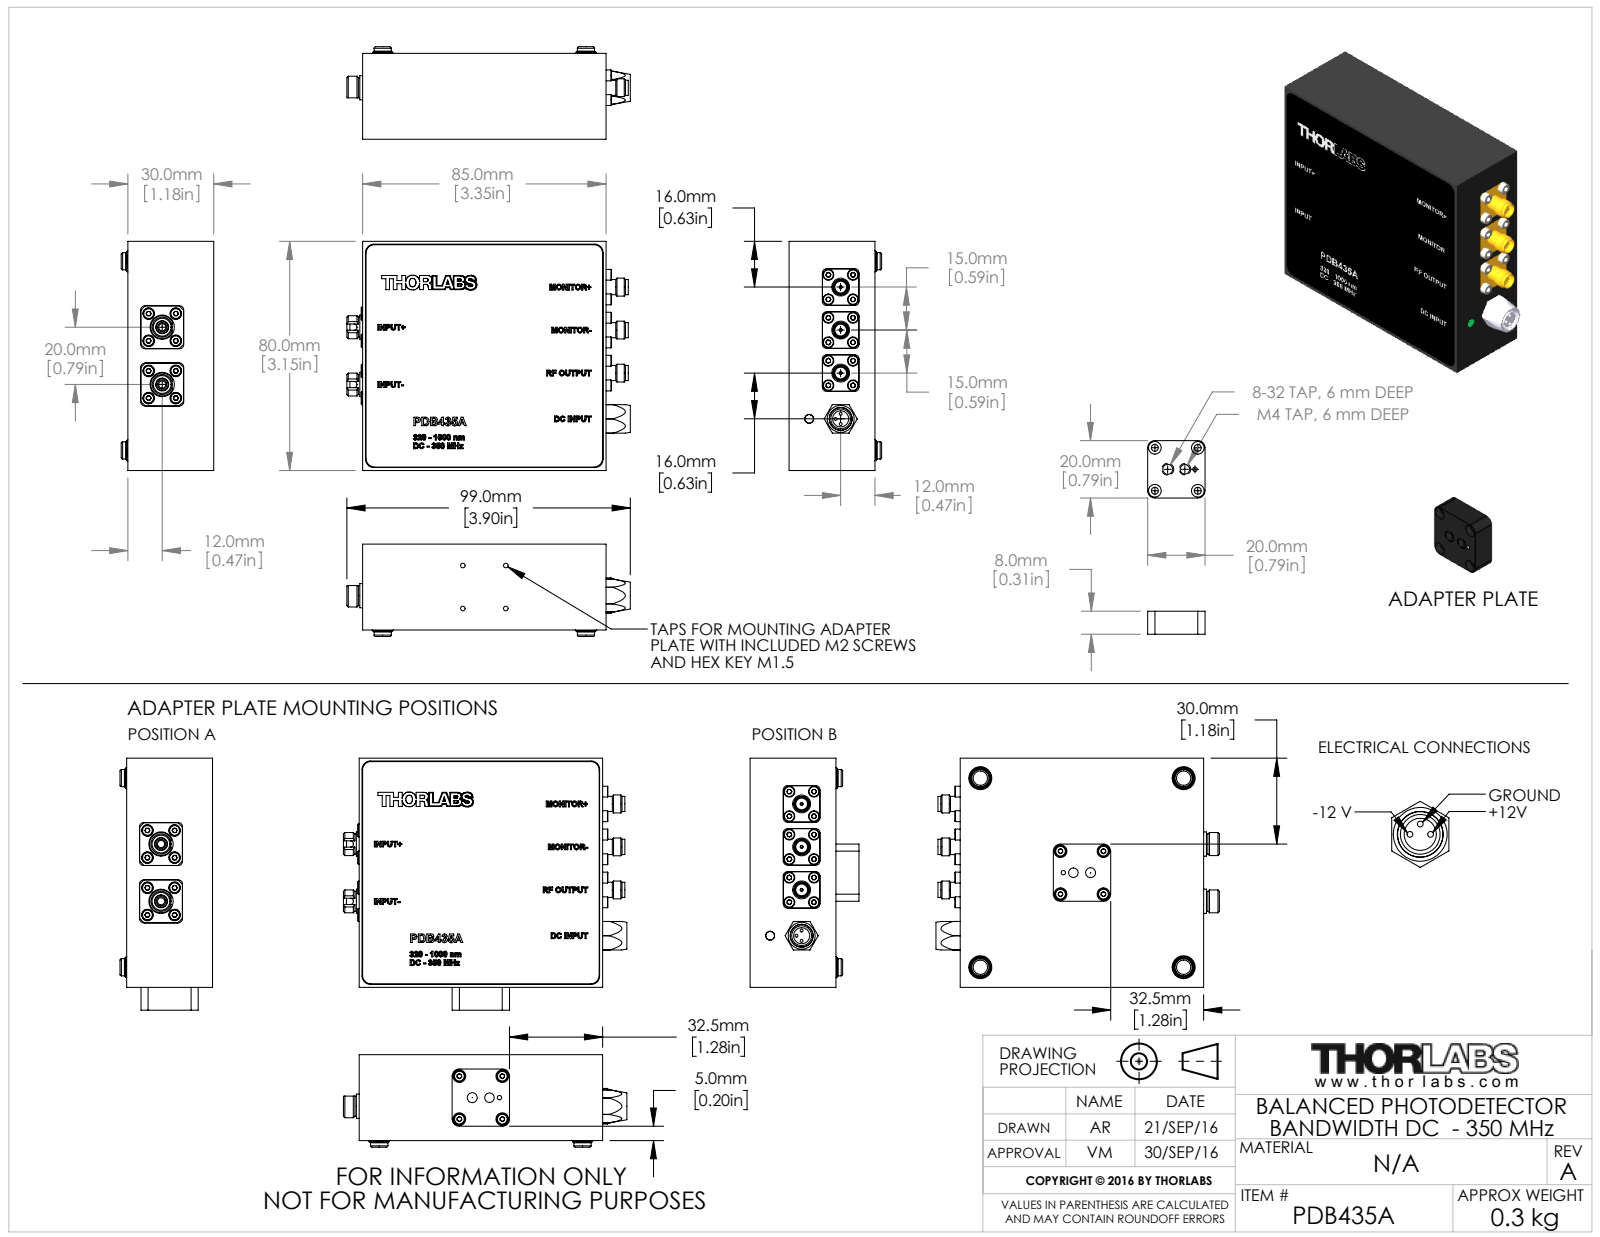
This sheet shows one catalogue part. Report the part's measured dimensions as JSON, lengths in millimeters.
{"part_name": "MTN005463-E0W", "step_written_by": "SolidWorks 2014 (AUTOMOTIVE_DESIGN)", "units": "millimeters", "bodies": {"solids": 90, "faces": 3049, "planar": 1756, "cylindrical": 584, "other": 709}, "overall_size": [99, 88, 38], "volume_mm3": 87719, "surface_area_mm2": 57809, "round_holes": [[1.6, 38], [2.6, 12], [2.2, 8], [2.4, 8], [4, 8], [4.4, 8], [1.02, 6], [8, 5], [0.8, 3], [1, 3], [4.1, 3], [4.2, 3]], "round_bosses_or_shafts": [[3.8, 20], [2, 20], [4.5, 8], [2.5, 8], [0.43, 6], [6, 4], [6.22, 3], [5.3, 3]], "partial_cylinders_radius": [[1.5, 20], [3, 12], [2.5, 8], [5, 8], [1, 4], [9.5, 2], [5.75, 1]], "face_to_face_distances": [29.7, 6, 23.7, 5.5, 80, 2, 74.5, 85, 3.5, 83], "hole_center_spacings": [15, 6.08, 8.6, 9.5, 6.72, 8.75, 11.53, 12.9]}
